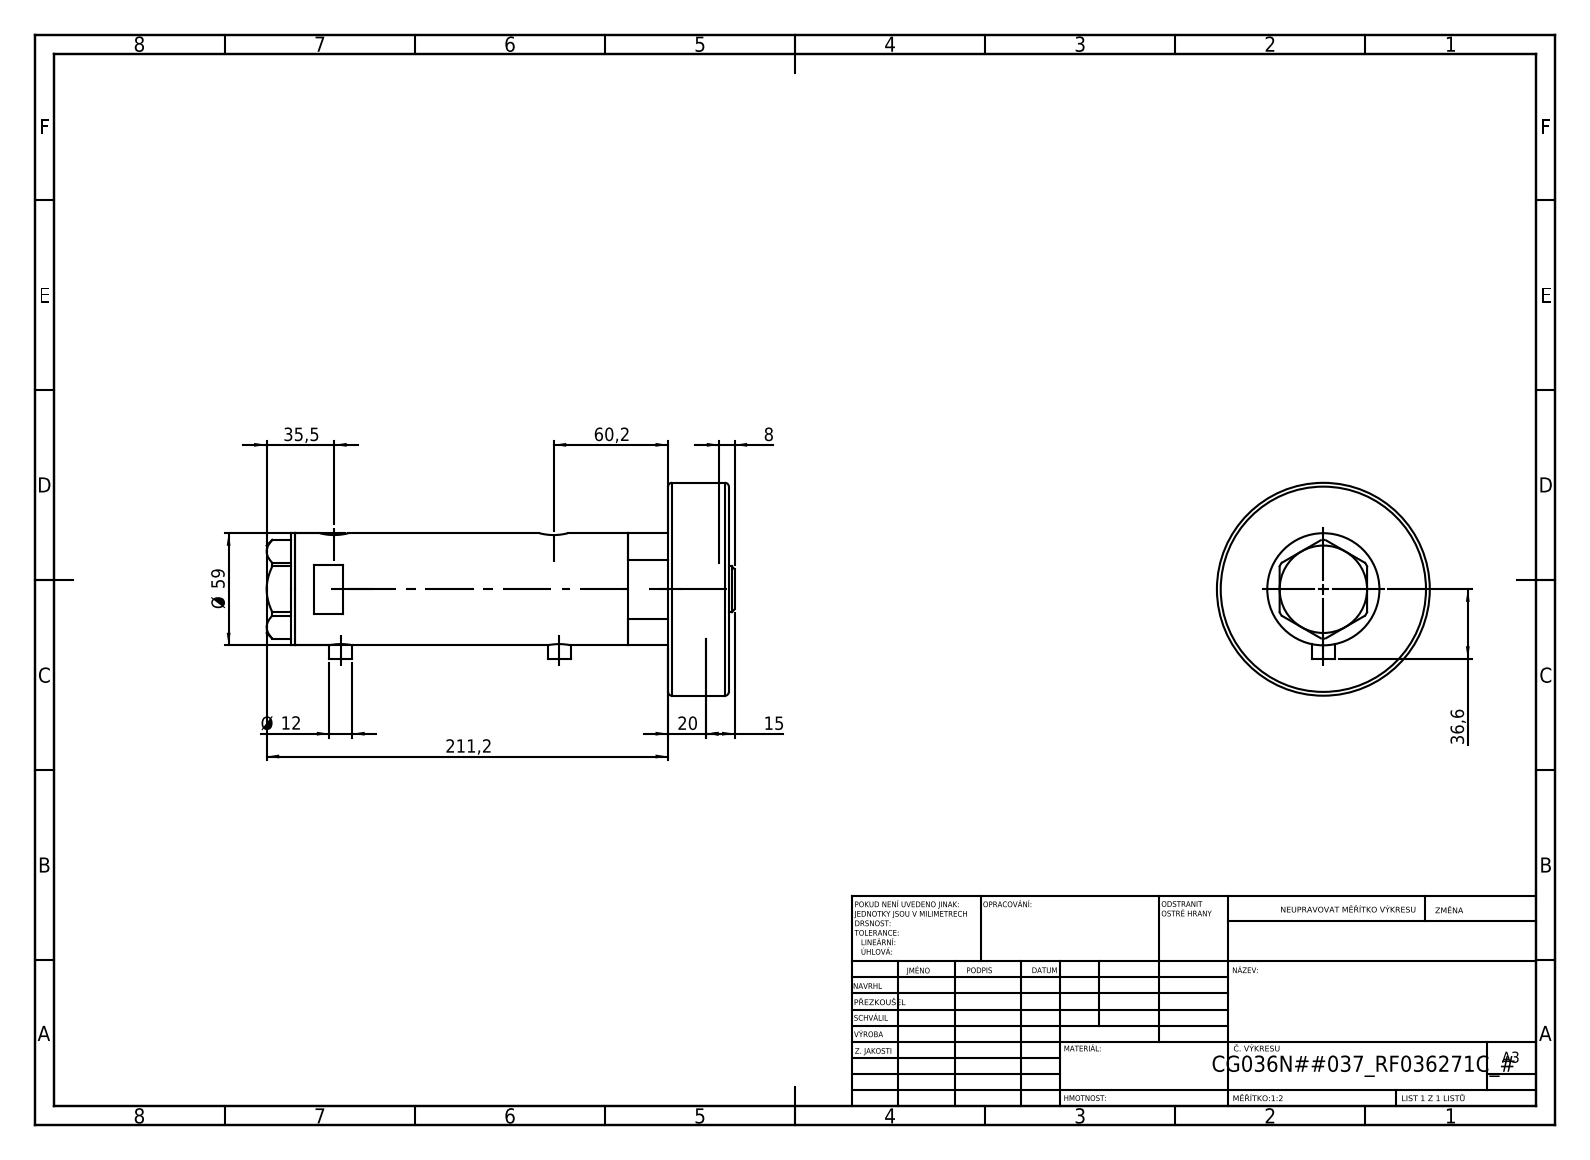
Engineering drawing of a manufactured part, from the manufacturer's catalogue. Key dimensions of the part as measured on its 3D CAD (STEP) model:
Part name (STEP PRODUCT): V270CG_VC; V270CG_271C; V270CG_BACK; V270CG_FRONT (+1 more)
STEP written by: SolidWorks 2019 (CONFIG_CONTROL_DESIGN)
Units: millimetres
Bodies: 5 solids, 130 faces (53 planar, 53 cylindrical, 24 other)
Overall size (bounding box): 246.2 × 112 × 112
Volume: 837 744 mm³ · Surface area: 146 391 mm²
Round holes (diameter × count): ⌀9.73 ×2, ⌀12.5 ×2, ⌀15 ×2, ⌀8.5 ×1, ⌀25 ×1, ⌀26.5 ×1, ⌀36 ×1, ⌀40 ×1, ⌀48 ×1, ⌀52 ×1
Round bosses / shafts (diameter × count): ⌀12 ×2, ⌀112 ×1, ⌀59 ×1, ⌀46 ×1, ⌀24 ×1
Main face-to-face distances: 32, 196.2, 228.2, 137.2, 59, 91, 23.5, 113.7, 172.7, 204.7
Hole centre spacings: 2.9, 3.5, 112, 114.9, 115.5, 118.4
